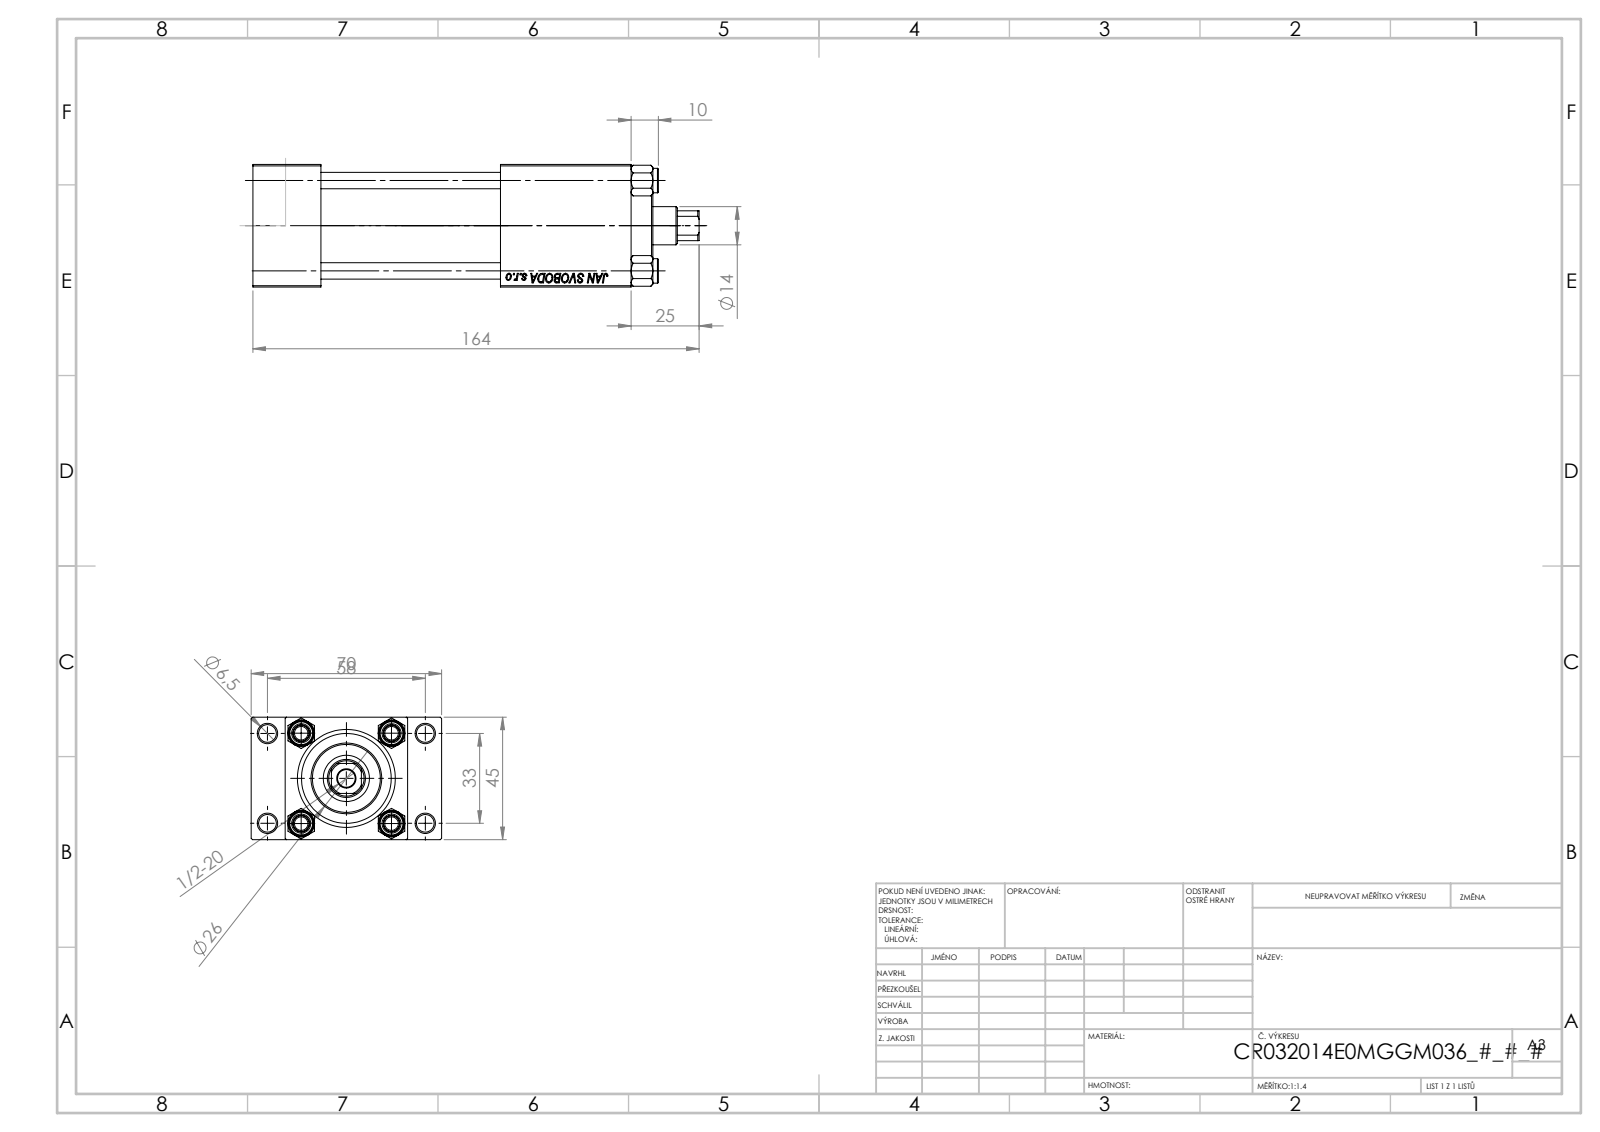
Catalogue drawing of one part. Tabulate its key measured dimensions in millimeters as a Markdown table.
| quantity | value |
| --- | --- |
| part name | V215CR_TYCINKA_E; NUT_M5_E; V215CR_E_Body; V215CR_VCP_E (+1 more) |
| STEP written by | SolidWorks 2019 (CONFIG_CONTROL_DESIGN) |
| units | millimeters |
| bodies | 11 solids, 1136 faces (497 planar, 87 cylindrical, 552 other) |
| overall size | 164 × 70 × 45 |
| volume | 229 623 mm³ |
| surface area | 81 501 mm² |
| round holes (diameter × count) | 6.5 × 5, 6 × 4, 7 × 2, 13.16 × 2, 20 × 2, 14 × 1, 17 × 1, 24 × 1, 32 × 1, 33 × 1 |
| round bosses / shafts (diameter × count) | 9 × 4, 38 × 1, 26 × 1 |
| partial cylindrical surfaces (radius × count) | 6.5 × 1 |
| main face-to-face distances | 45, 25, 12.5, 57.5, 139, 114, 70, 91, 66, 48 |
| hole center spacings | 12.4, 23.48, 33.2, 33.37, 35.35, 45.6, 56.35, 33 |
